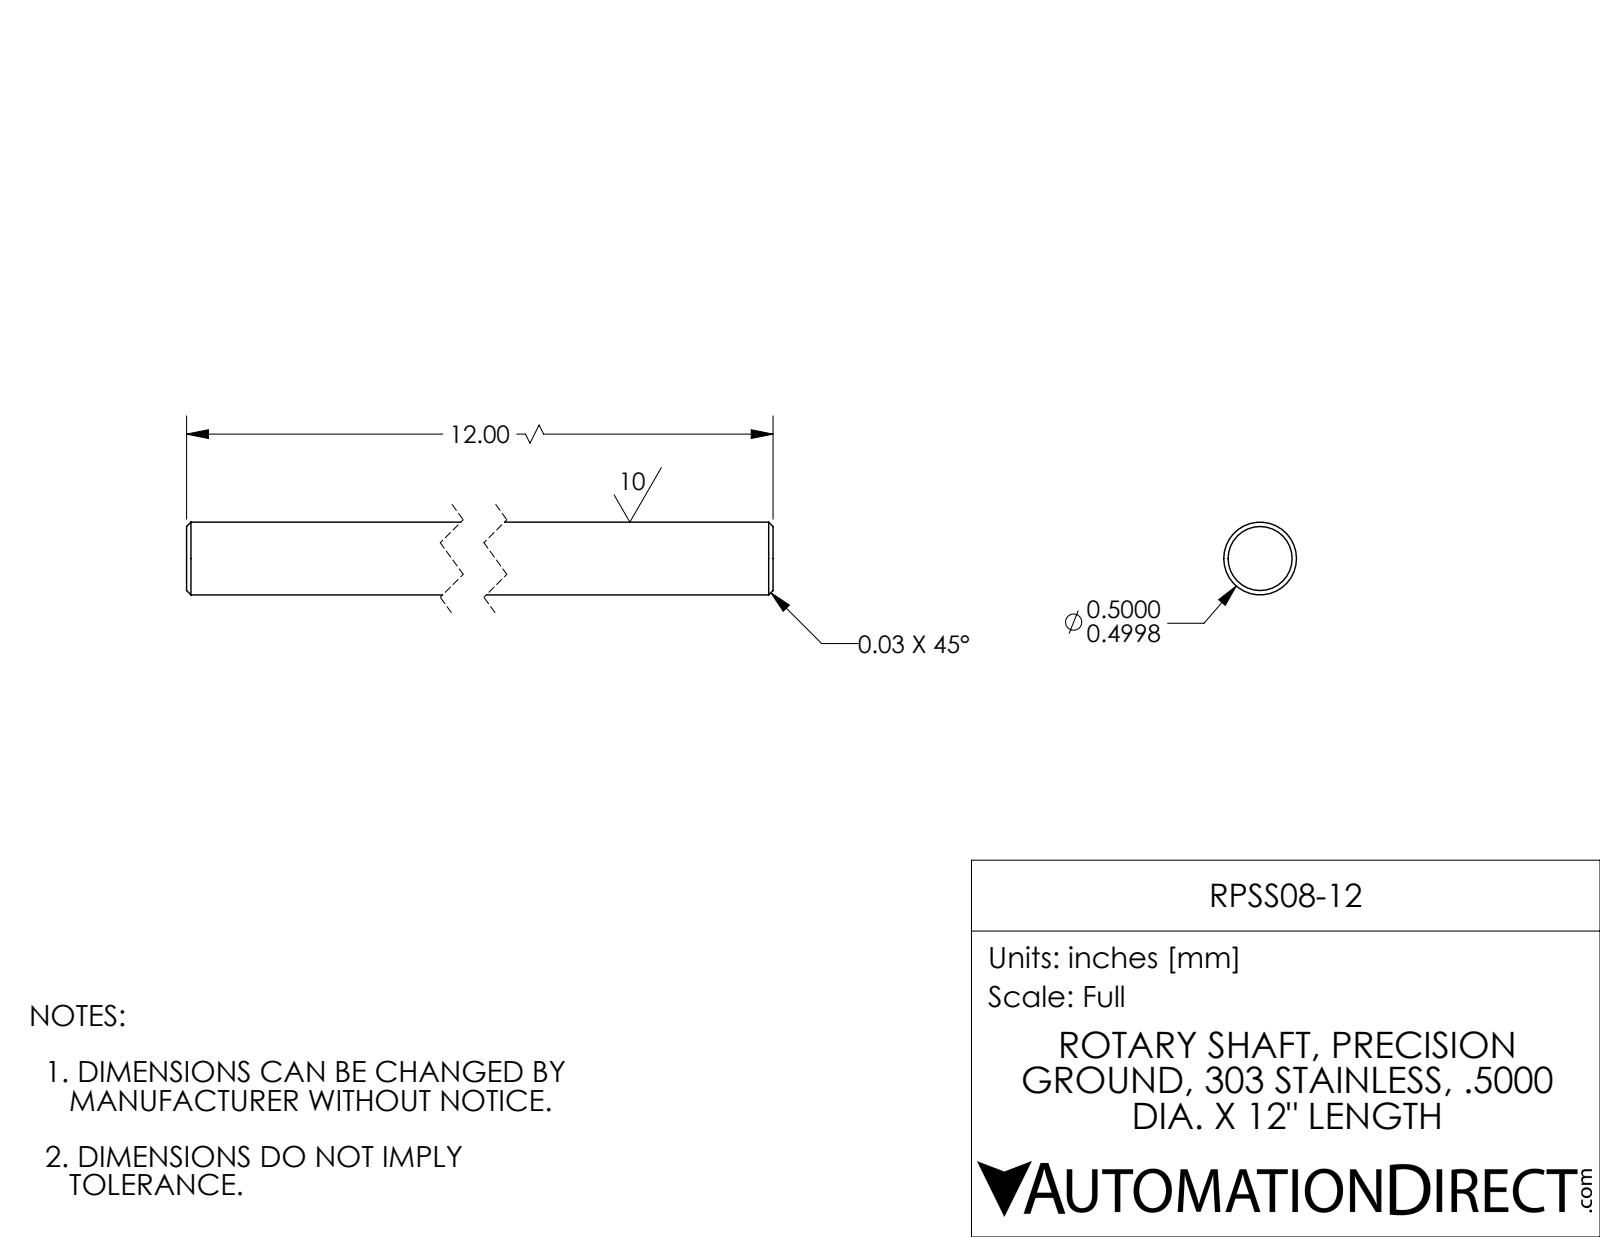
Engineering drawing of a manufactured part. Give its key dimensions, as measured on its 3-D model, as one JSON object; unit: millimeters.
{"part_name": "RPSS08-12", "step_written_by": "SolidWorks 2017 (AUTOMOTIVE_DESIGN)", "units": "millimeters", "bodies": {"solids": 1, "faces": 8, "planar": 2, "cylindrical": 2, "other": 4}, "overall_size": [304.8, 12.7, 12.7], "volume_mm3": 38590, "surface_area_mm2": 12370, "round_bosses_or_shafts": [[12.7, 1]], "face_to_face_distances": [304.8]}
